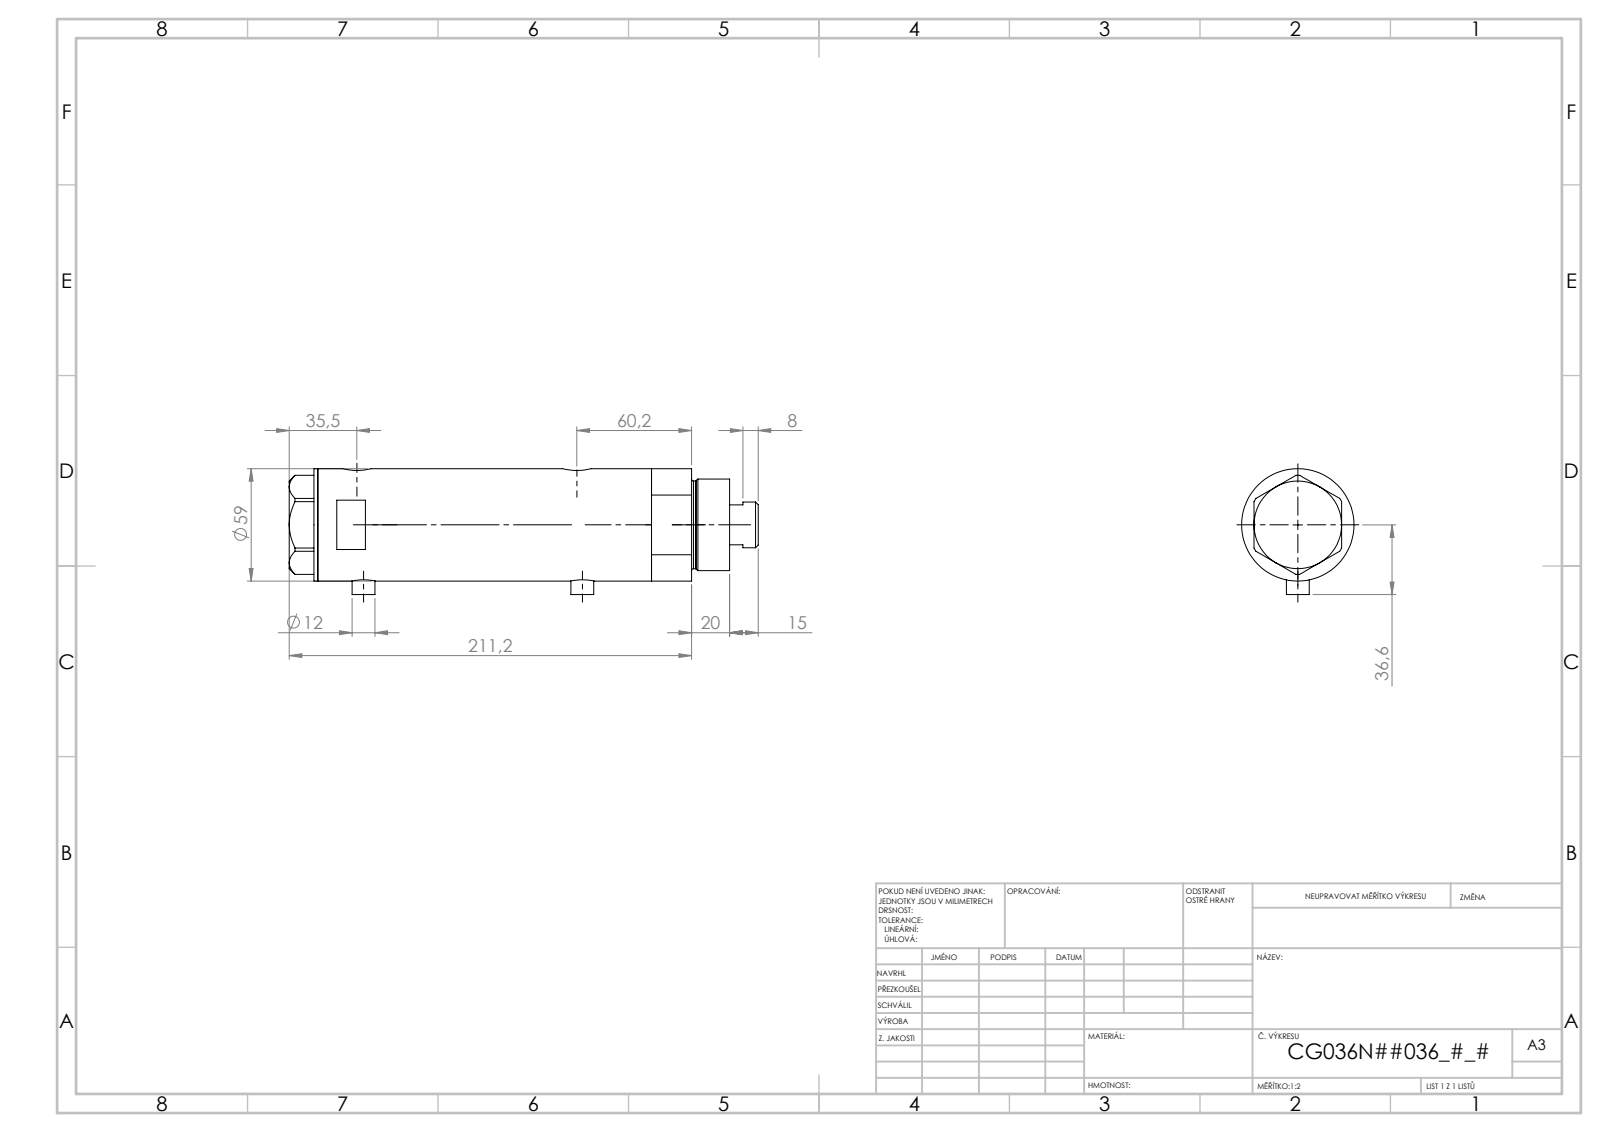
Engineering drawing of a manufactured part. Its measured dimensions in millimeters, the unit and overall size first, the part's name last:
Units: millimetres
Overall size (bounding box): 199.42 × 60.1 × 59
Round holes (diameter × count): ⌀5 ×2, ⌀9.73 ×2, ⌀12.5 ×2, ⌀15 ×2, ⌀8.5 ×1, ⌀25 ×1, ⌀26.5 ×1, ⌀36 ×1, ⌀40 ×1, ⌀52 ×1
Round bosses / shafts (diameter × count): ⌀12 ×2, ⌀59 ×1, ⌀48 ×1, ⌀46 ×1, ⌀24 ×1
Main face-to-face distances: 93.34, 23.5, 69.84, 15, 38.5, 108.34, 184.42, 169.42, 145.92, 76.08
Hole centre spacings: 2.9, 3.5, 68.15, 71.05, 71.65, 74.55, 2.89, 2.91
Volume: 450 592 mm³ · Surface area: 95 465 mm²
Bodies: 4 solids, 126 faces (53 planar, 53 cylindrical, 20 other)
Part name (STEP PRODUCT): V270CG_VC; V270CG_FRONT; V270CG_MIDDLE; V270CG_BACK
STEP written by: SolidWorks 2019 (CONFIG_CONTROL_DESIGN)
